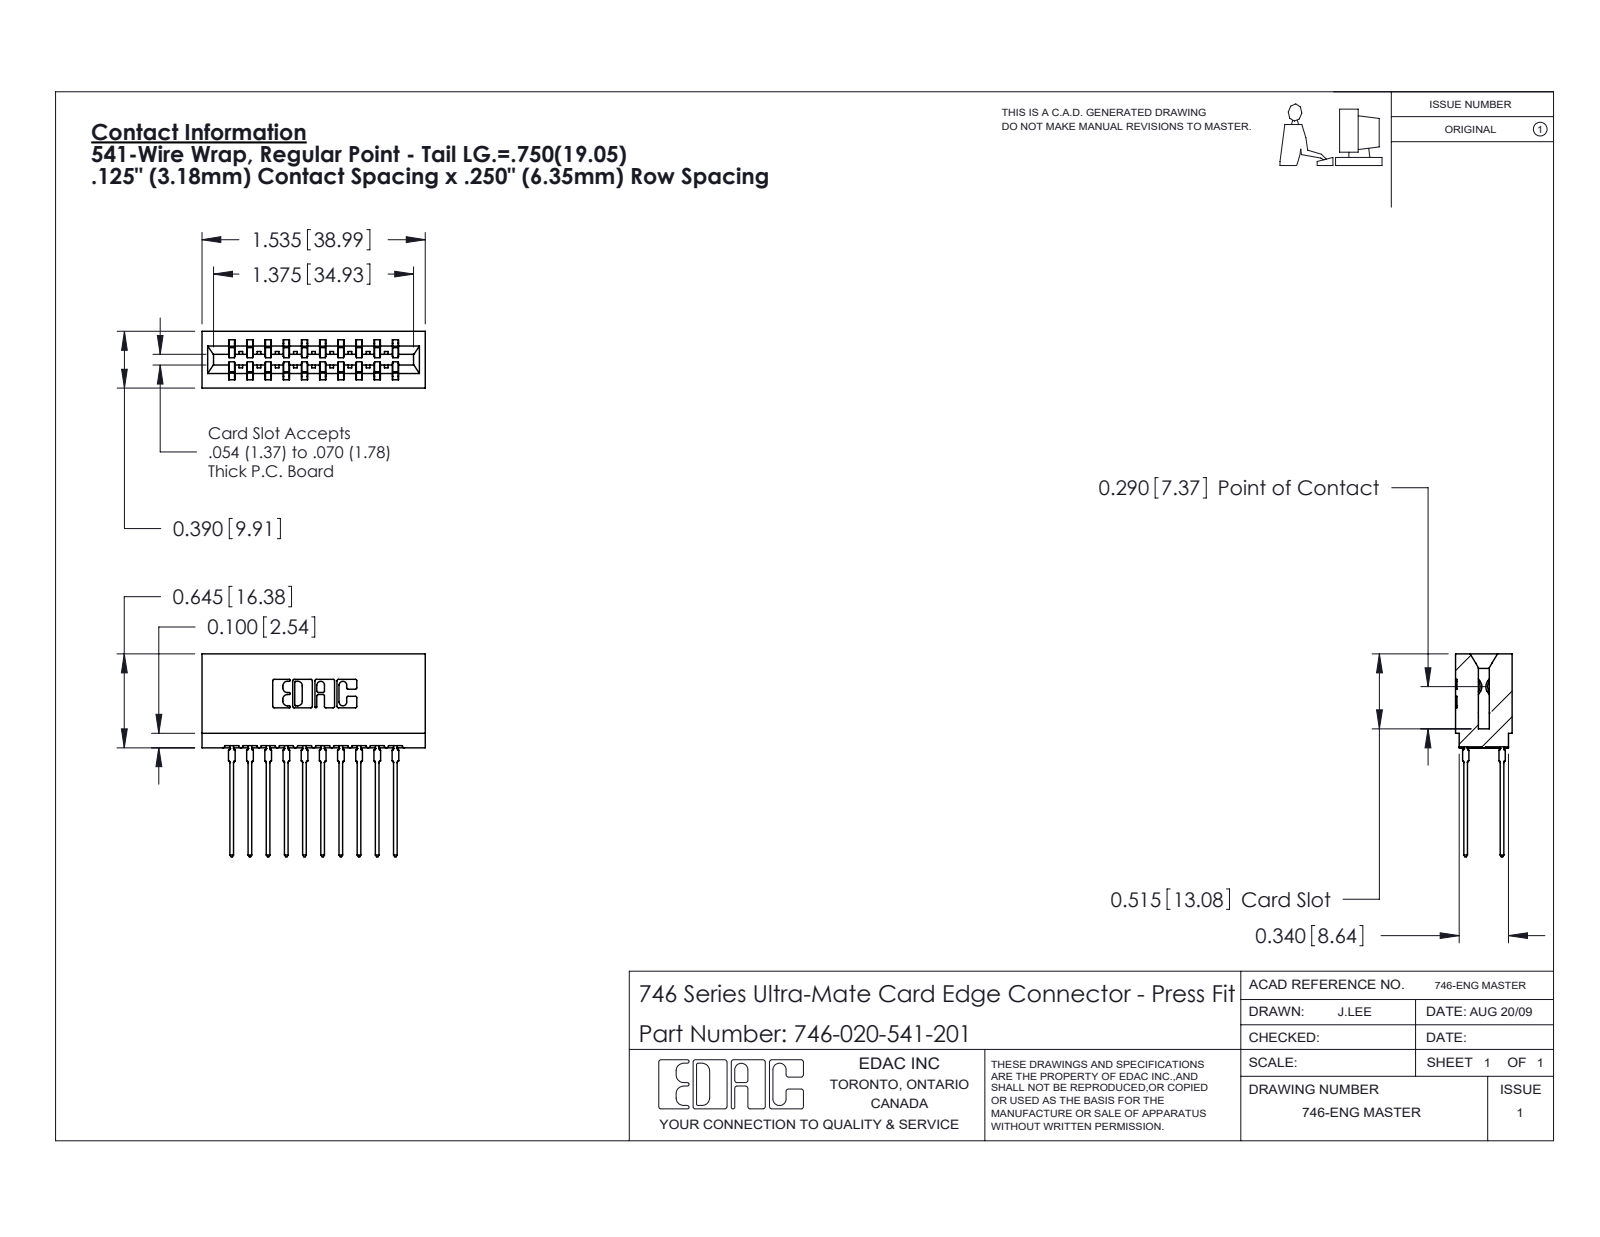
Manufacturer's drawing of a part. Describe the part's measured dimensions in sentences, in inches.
The part is named "746-292-001_541; 746-020-541-201; 746 Part_.515 Slot Depth - 01". Its 3-D file was written by "SolidWorks 2020 (CONFIG_CONTROL_DESIGN)". It is 21 solids with 1887 faces: 975 planar, 392 cylindrical and 520 other. Overall it measures 1.535 by 1.394 by 0.39 inches. Its volume is 0.274 cubic inches and its surface area 10.99 square inches. Partial cylindrical surfaces (rounded edges, fillets, slot ends): 40 of radius 0.021, 22 of radius 0.01, 11 of radius 0.015, 8 of radius 0.005, 8 of radius 0.011, 6 of radius 0.007, 6 of radius 0.031, 3 of radius 0.026. The main face-to-face distances are 0.25, 0.333, 0.057, 0.5, 0.125, 0.042, 0.083, 0.025, 0.375, 0.208.
